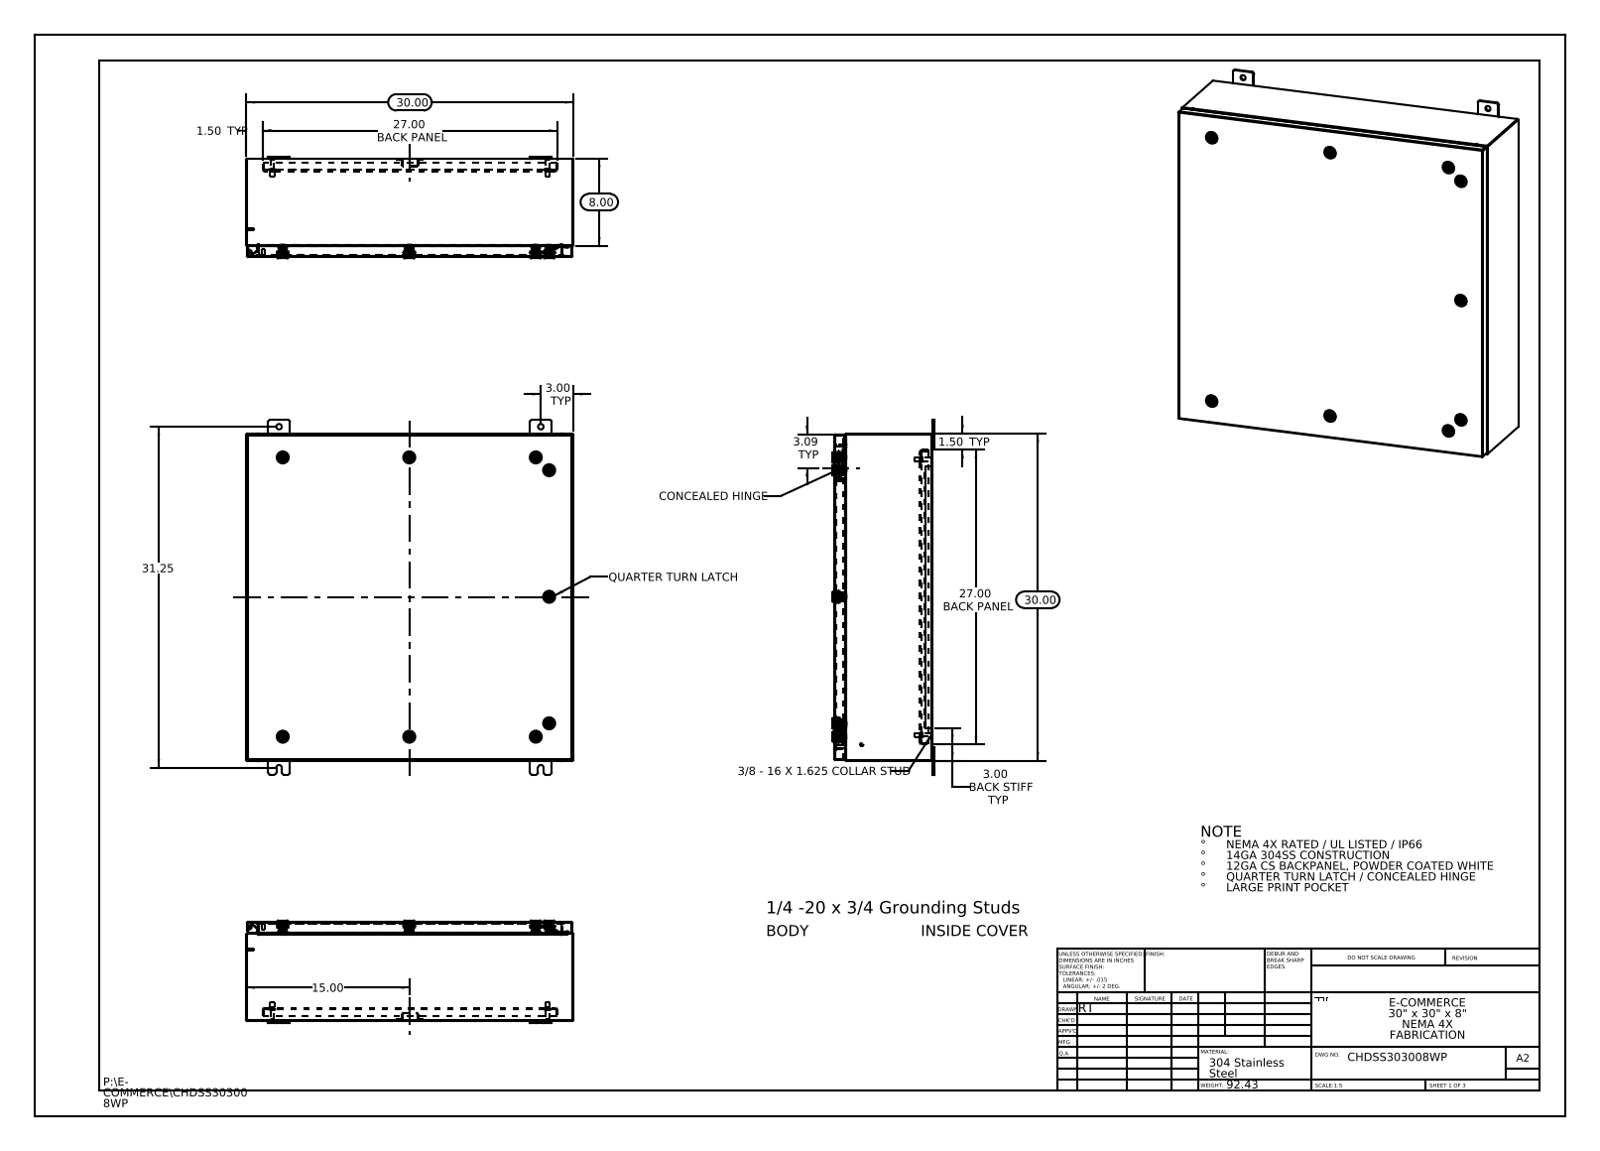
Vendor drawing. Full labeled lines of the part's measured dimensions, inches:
Part name (STEP PRODUCT): Washer-221320-IB-Industrilas_Washer-221320-IB-Industrilas; CHDSS303008WP Top; Screw-221320-IB-Industrilas_Screw-221320-IB-Industrilas; CHDSS303008WP Body (+8 more)
STEP written by: SolidWorks 2013 (CONFIG_CONTROL_DESIGN)
Units: inches
Bodies: 73 solids, 7894 faces (2266 planar, 2454 cylindrical, 3174 other)
Overall size (bounding box): 32.5 × 30 × 9.356
Volume: 328.9 in³ · Surface area: 8 149 in²
Round holes (diameter × count): ⌀0.197 ×9, ⌀0.394 ×9, ⌀0.4 ×9, ⌀0.63 ×9, ⌀0.787 ×9, ⌀0.5 ×8, ⌀0.136 ×4, ⌀0.211 ×1
Round bosses / shafts (diameter × count): ⌀0.236 ×11, ⌀1.102 ×9, ⌀0.78 ×9, ⌀0.626 ×9, ⌀0.61 ×9, ⌀0.531 ×9, ⌀0.392 ×9, ⌀0.114 ×9
Partial cylindrical surfaces — rounded edges, fillets, slot ends (radius × count): R0.006 ×297, R0.118 ×297, R0.028 ×108, R0.02 ×36, R0.197 ×36, R0.013 ×26, R0.19 ×24, R0.088 ×22
Main face-to-face distances: 0.075, 0.074, 29.925, 9.01, 8.935, 8.936, 8.861, 0.104, 1, 1.075
Hole centre spacings: 11.6, 28.106, 23.2, 25.6, 1.858, 12.883, 24, 24.456
